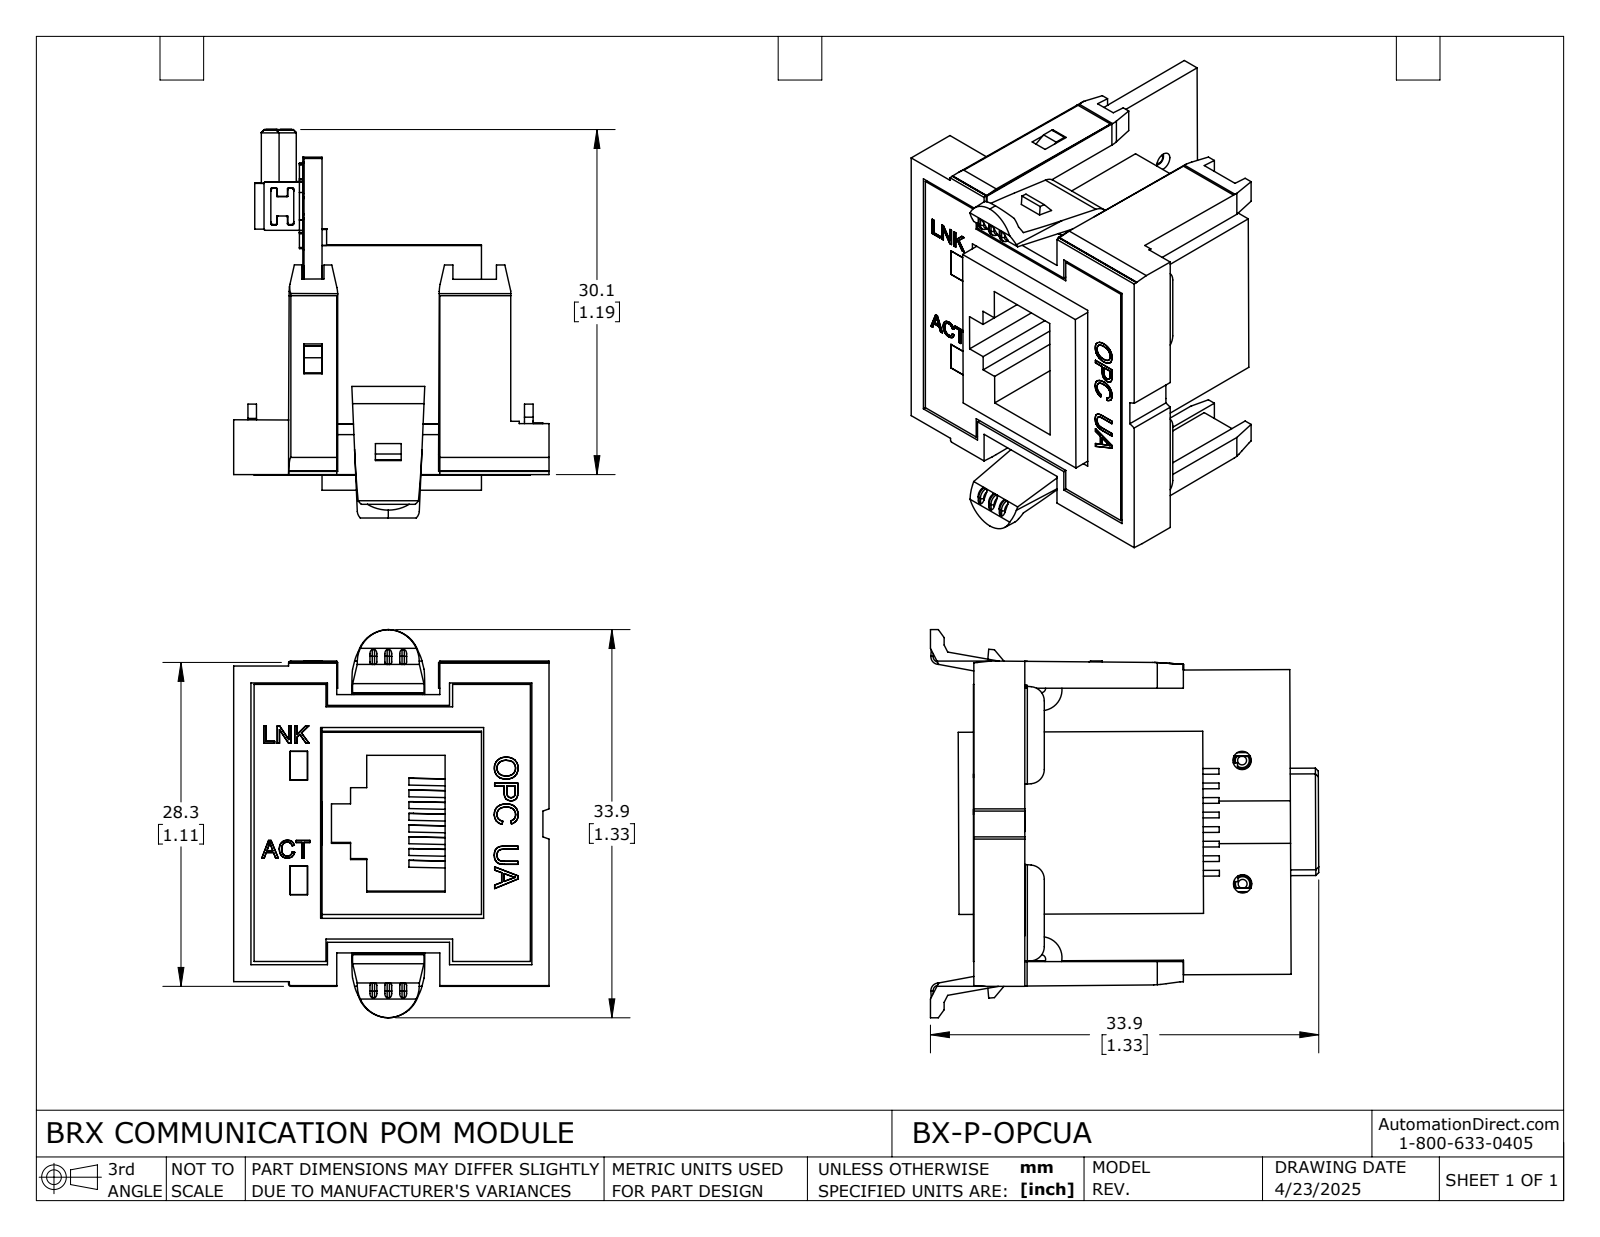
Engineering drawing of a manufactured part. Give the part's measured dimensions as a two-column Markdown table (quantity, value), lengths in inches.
| quantity | value |
| --- | --- |
| part name | BX-P-OPCUA |
| STEP written by | SolidWorks 2021 (AUTOMOTIVE_DESIGN) |
| units | inches |
| bodies | 24 solids, 1586 faces (1242 planar, 159 cylindrical, 185 other) |
| overall size | 1.335 × 1.334 × 1.084 |
| volume | 0.393 in³ |
| surface area | 14.42 in² |
| round holes (diameter × count) | 0.037 × 3, 0.063 × 2 |
| round bosses / shafts (diameter × count) | 0.118 × 2 |
| partial cylindrical surfaces (radius × count) | 0.004 × 40, 0.008 × 27, 0.006 × 8, 0.049 × 5, 0.01 × 4, 0.108 × 4, 0.02 × 3, 0.03 × 3 |
| main face-to-face distances | 0.02, 0.062, 0.61, 0.548, 0.626, 0.066, 0.021, 0.066, 0.485, 0.423 |
| hole center spacings | 0.552, 0.687, 0.196, 0.197, 0.394, 0.424, 0.591, 0.592 |
